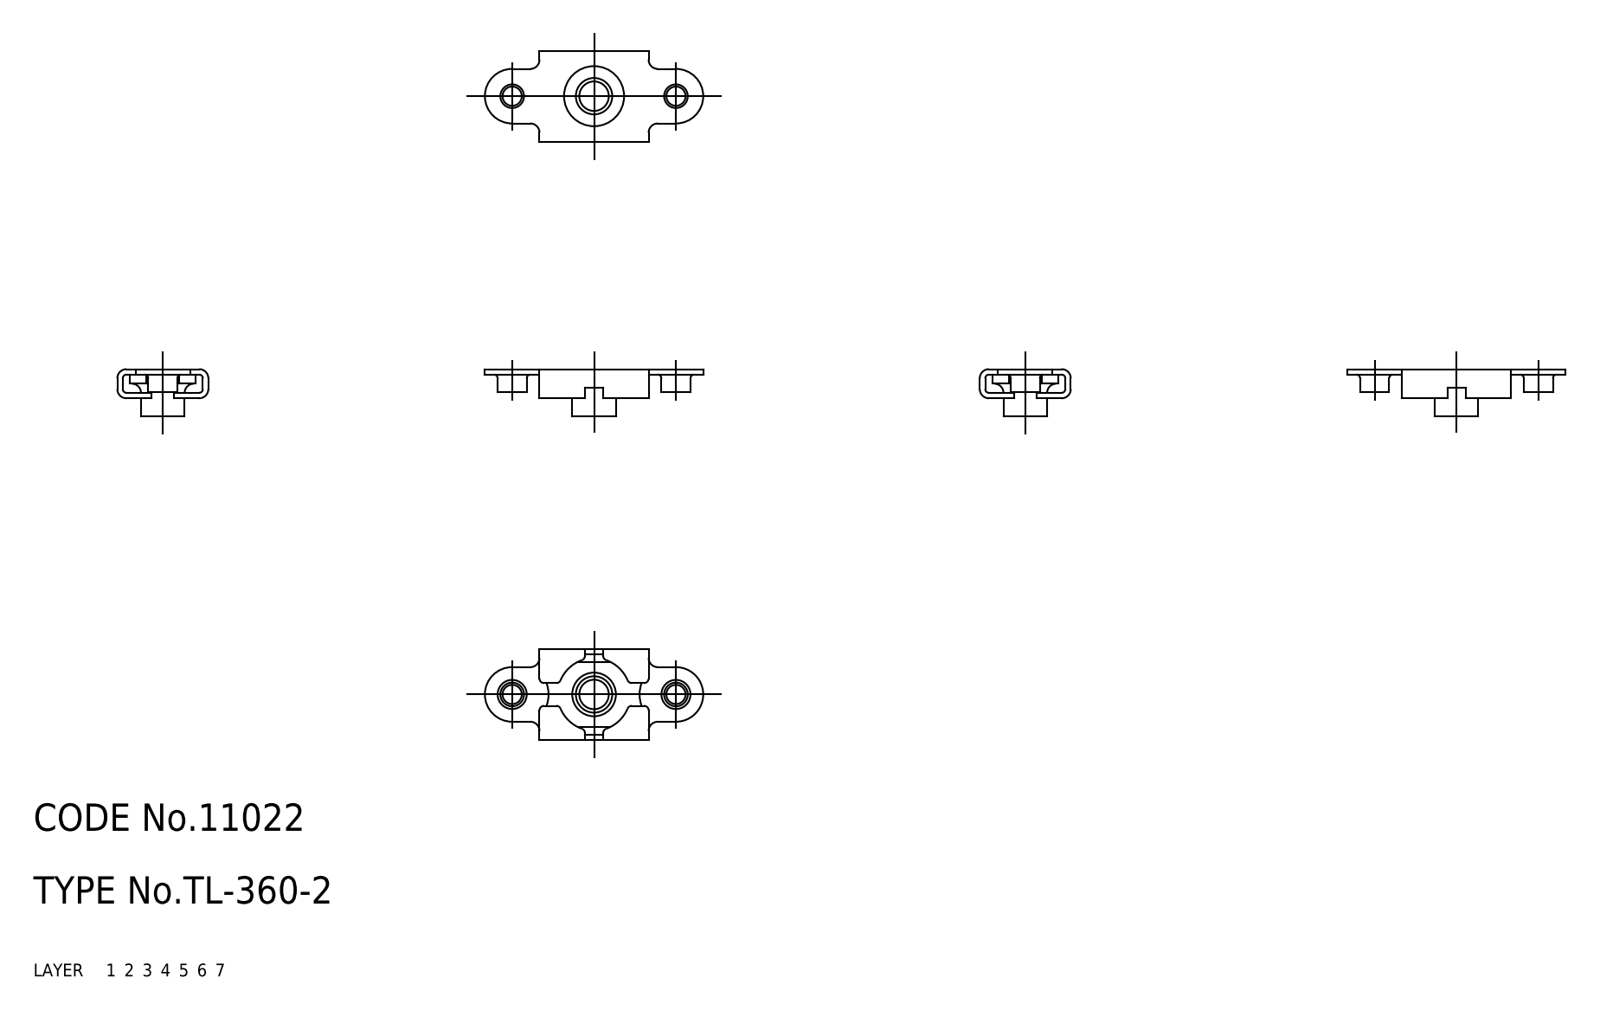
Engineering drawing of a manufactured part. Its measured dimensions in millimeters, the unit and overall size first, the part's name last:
Units: millimetres
Overall size (bounding box): 24 × 10 × 5.2
Volume: 222 mm³ · Surface area: 854 mm²
Bodies: 2 solids, 110 faces (0 planar, 0 cylindrical, 110 other)
Part name (STEP PRODUCT): 67114710; 67114723
STEP written by: CADfix (AUTOMOTIVE_DESIGN)
